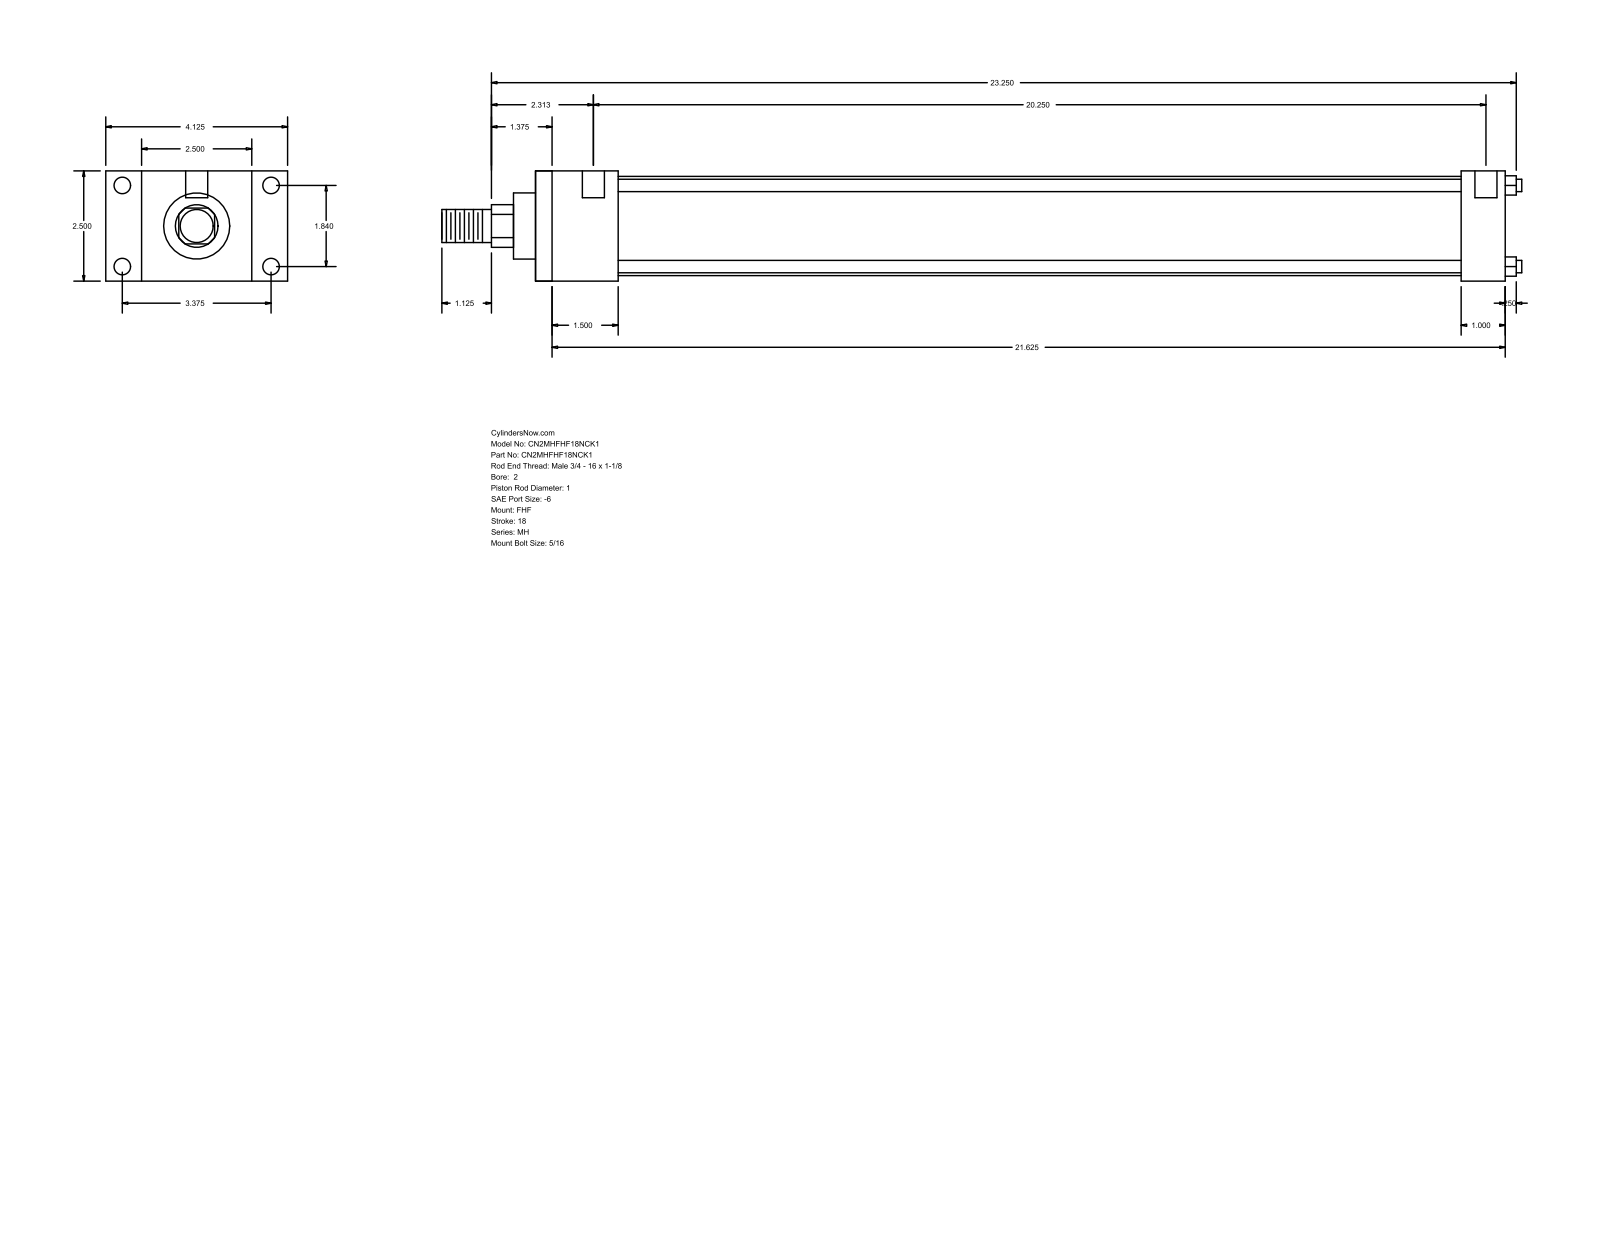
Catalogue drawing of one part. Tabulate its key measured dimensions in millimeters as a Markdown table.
| quantity | value |
| --- | --- |
| part name | MH_FHF__0200_1 |
| STEP written by | GSSL Pune (CONFIG_CONTROL_DESIGN) |
| units | millimeters |
| bodies | 0 solids, 88 faces (60 planar, 28 cylindrical, 0 other) |
| overall size | 622.3 × 104.78 × 63.5 |
| round holes (diameter × count) | 5.56 × 4, 9.53 × 4, 12.7 × 2 |
| round bosses / shafts (diameter × count) | 7.14 × 4, 57.15 × 1, 38.1 × 1, 25.4 × 1, 19.05 × 1 |
| partial cylindrical surfaces (radius × count) | 12.29 × 1 |
| main face-to-face distances | 63.5, 558.8, 47.63, 511.17, 20.64, 84.14, 104.78, 25.4, 533.4, 485.77 |
| hole center spacings | 46.74, 85.72, 97.63, 522.28, 3.17, 4.76, 514.35, 517.52 |
